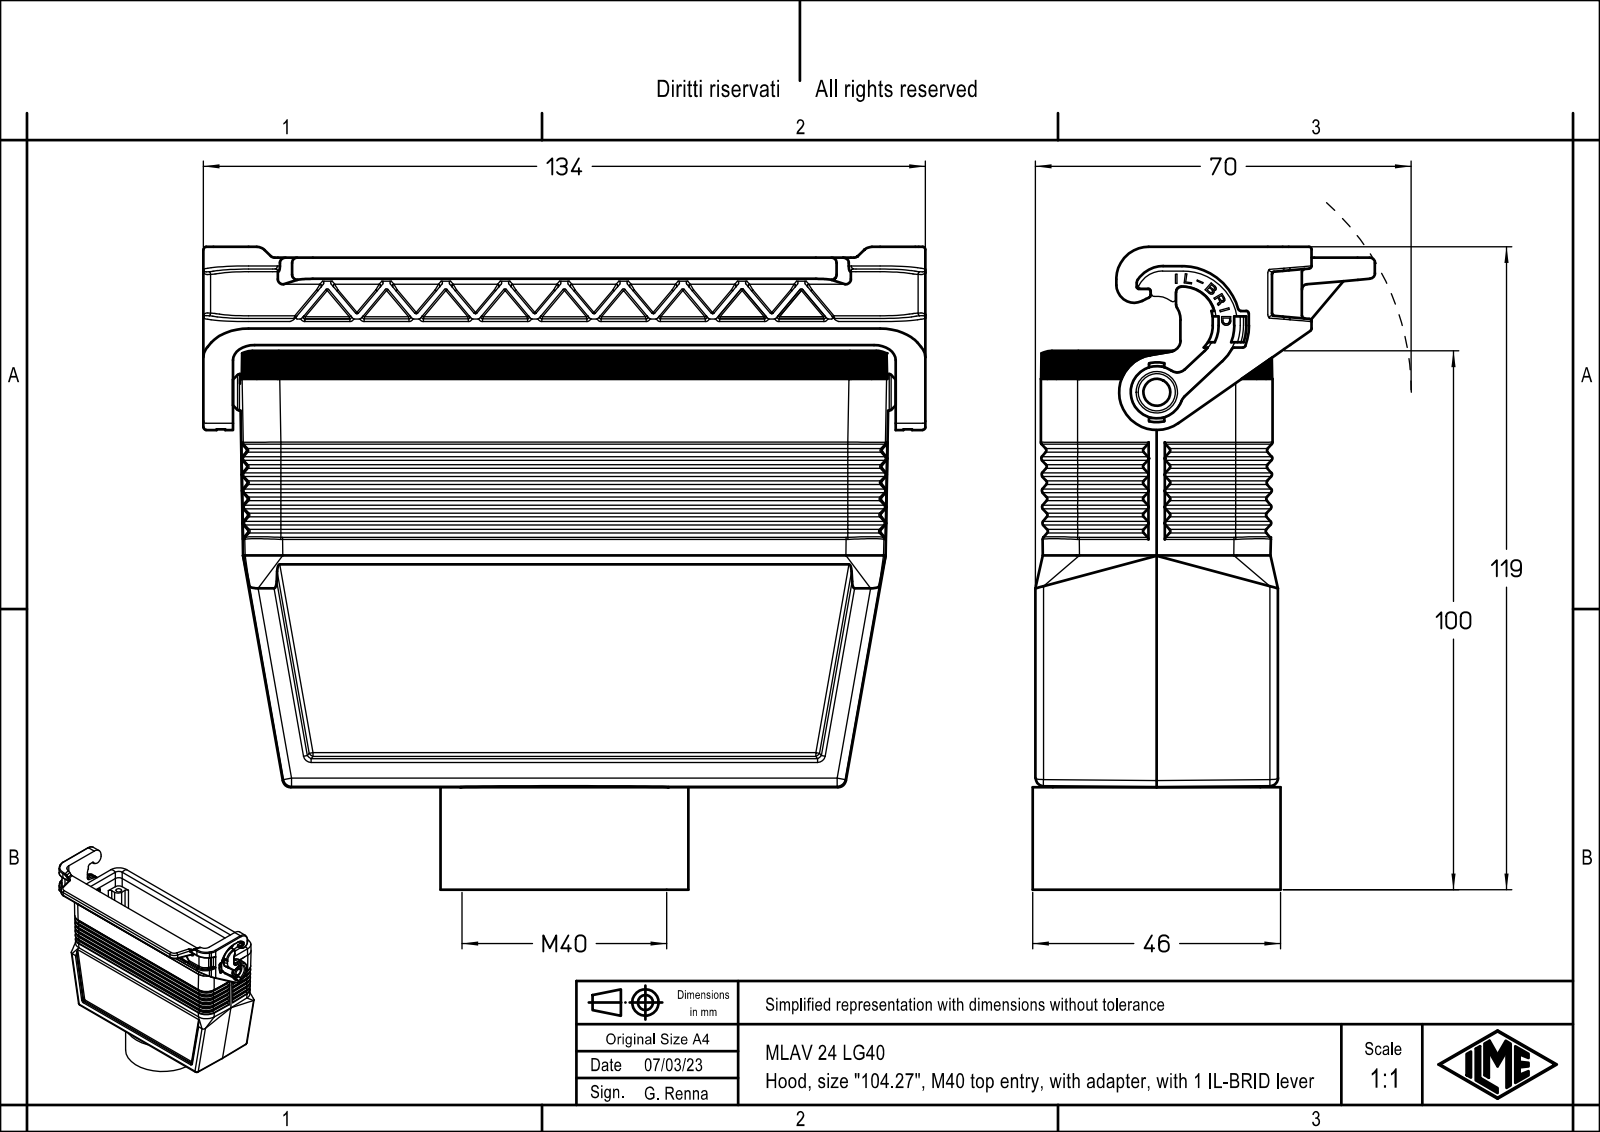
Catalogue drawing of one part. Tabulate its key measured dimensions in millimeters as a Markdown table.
| quantity | value |
| --- | --- |
| part name | MLAV 24 LG40 |
| STEP written by | Creo Elements/Direct Modeling 20.1B 02-Apr-2019 (C) Parametric Technology GmbH (AUTOMOTIVE_DESIGN) |
| units | millimeters |
| bodies | 1 solid, 1430 faces (805 planar, 375 cylindrical, 250 other) |
| overall size | 134 × 119.25 × 63.5 |
| volume | 139 776 mm³ |
| surface area | 78 834 mm² |
| round holes (diameter × count) | 3 × 4, 3.5 × 4, 3.25 × 1, 5.4 × 1, 7.7 × 1, 34 × 1, 38.6 × 1 |
| round bosses / shafts (diameter × count) | 46 × 1, 38.5 × 1, 6.9 × 1, 6.8 × 1, 5.2 × 1, 3.2 × 1 |
| partial cylindrical surfaces (radius × count) | 0.5 × 77, 0.1 × 27, 1.5 × 23, 1 × 16, 0.2 × 15, 7 × 14, 0.33 × 13, 3 × 12 |
| main face-to-face distances | 3.75, 39.25, 35.5, 43, 2, 7, 46.25, 3.25, 42.5, 1 |
| hole center spacings | 53.72, 27, 104, 107.45 |
